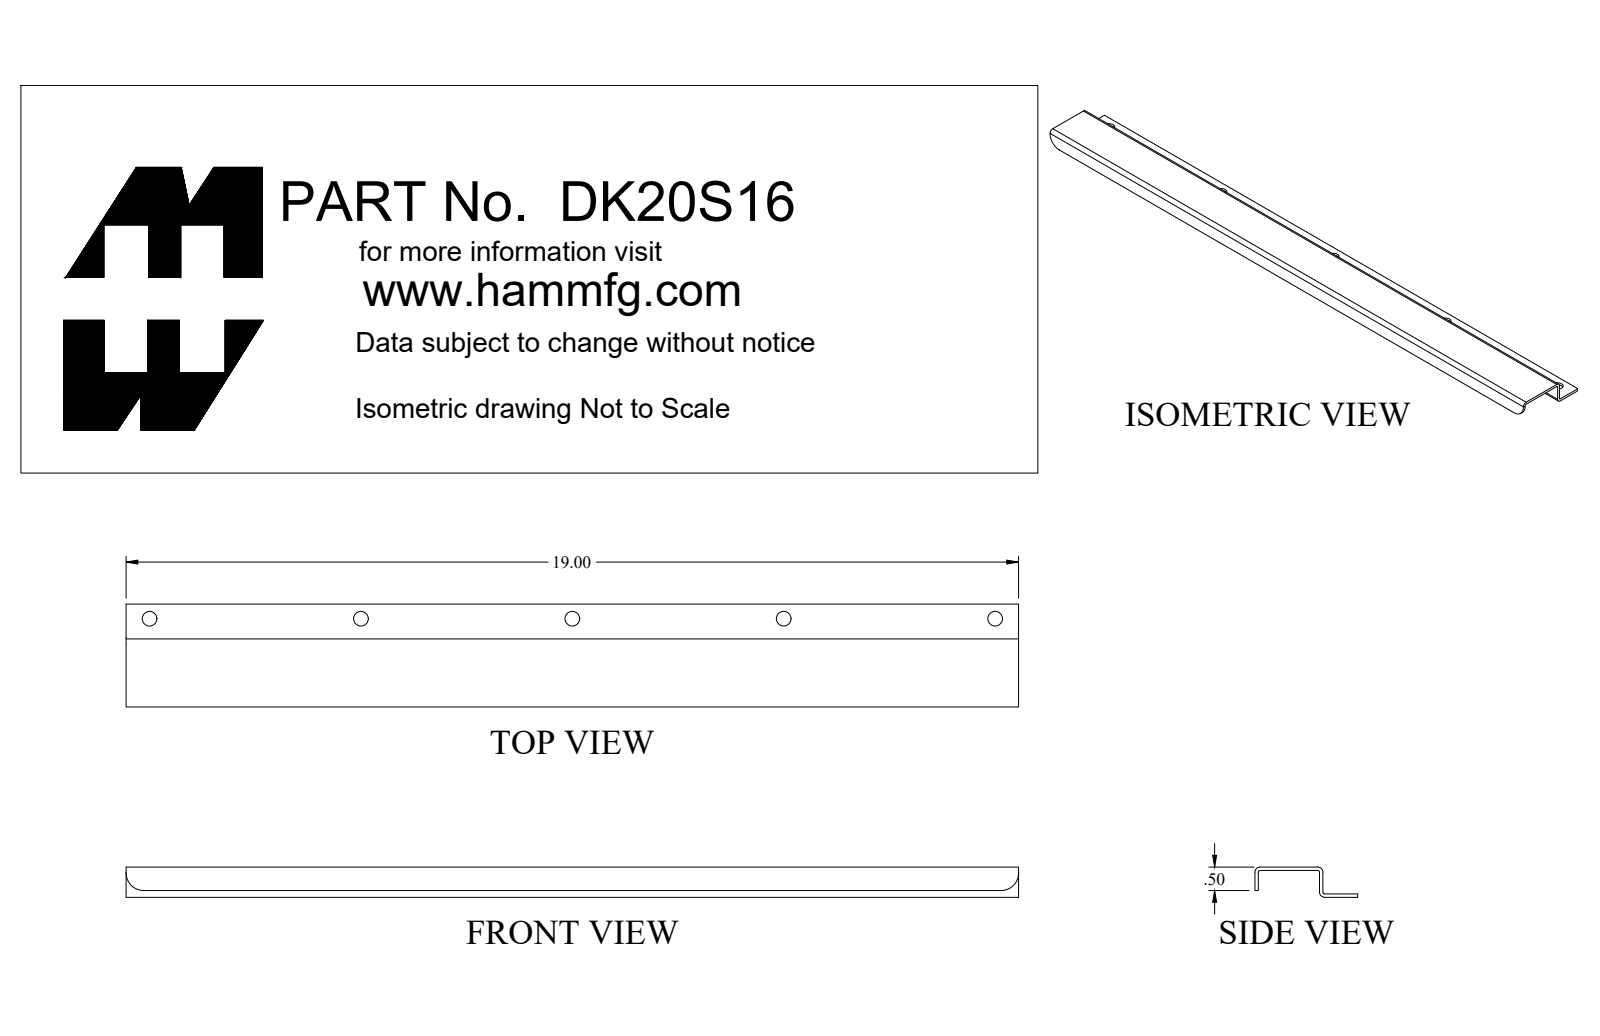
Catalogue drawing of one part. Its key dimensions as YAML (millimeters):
part_name: "DK20S16_Default"
step_written_by: "SolidWorks 2018 (CONFIG_CONTROL_DESIGN)"
units: millimeters
bodies: {solids: 5, faces: 69, planar: 35, cylindrical: 28, other: 6}
overall_size: [482.6, 55.6, 33.6]
volume: 85410
surface_area: 99290
round_holes:
  - {diameter: 8, count: 5}
  - {diameter: 5.1, count: 1}
  - {diameter: 7, count: 1}
round_bosses_or_shafts:
  - {diameter: 15.9, count: 1}
  - {diameter: 12.3, count: 1}
  - {diameter: 6.4, count: 1}
partial_cylinders:
  - {radius: 0.9, count: 3}
  - {radius: 2.7, count: 3}
  - {radius: 9.5, count: 2}
face_to_face_distances: [1.8, 14.5, 16.4, 35, 12.7, 1.6, 16.1, 18, 3.4, 36.8]
hole_center_spacings: [114.3, 228.6, 342.9, 457.2]
